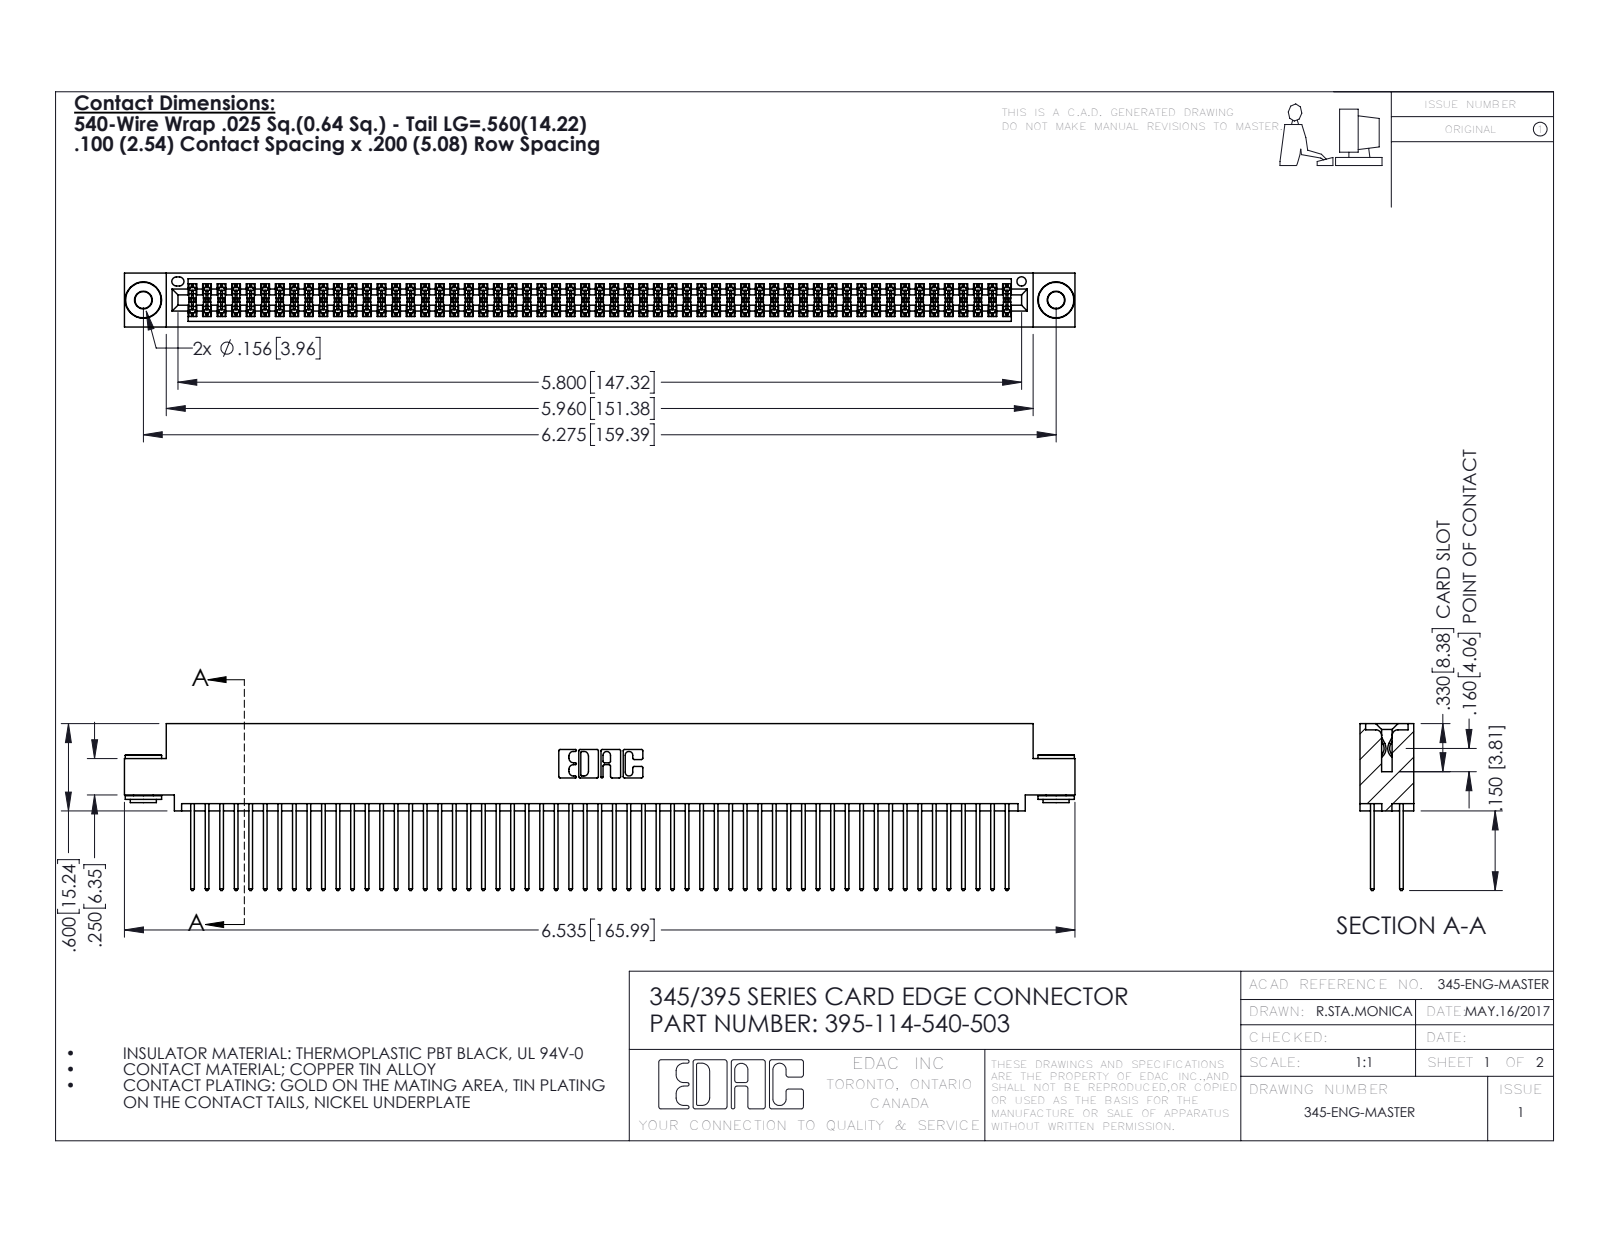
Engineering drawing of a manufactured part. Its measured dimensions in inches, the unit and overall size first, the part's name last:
Units: inches
Overall size (bounding box): 6.535 × 1.147 × 0.37
Round holes (diameter × count): ⌀0.116 ×2, ⌀0.156 ×2, ⌀0.064 ×1
Round bosses / shafts (diameter × count): ⌀0.25 ×2, ⌀0.18 ×2, ⌀0.136 ×2
Partial cylindrical surfaces — rounded edges, fillets, slot ends (radius × count): R0.006 ×171, R0.01 ×114, R0.01 ×22, R0.007 ×6, R0.031 ×6, R0.026 ×3, R0.014 ×2, R0.019 ×2
Main face-to-face distances: 0.072, 0.298, 0.2, 0.025, 0.098, 0.272, 0.37, 0.225, 0.175, 0.149
Hole centre spacings: 0.27, 6.039, 6.275
Volume: 1.016 in³ · Surface area: 42.15 in²
Bodies: 117 solids, 5868 faces (3856 planar, 2004 cylindrical, 8 other)
Part name (STEP PRODUCT): 395-114-540-503; 345-250-002_345-250-002-102; 345 Part_0.110 Offset - 0.156 Dia-TH; 345-292-001_345-293-140
STEP written by: SolidWorks 2016 (CONFIG_CONTROL_DESIGN)
